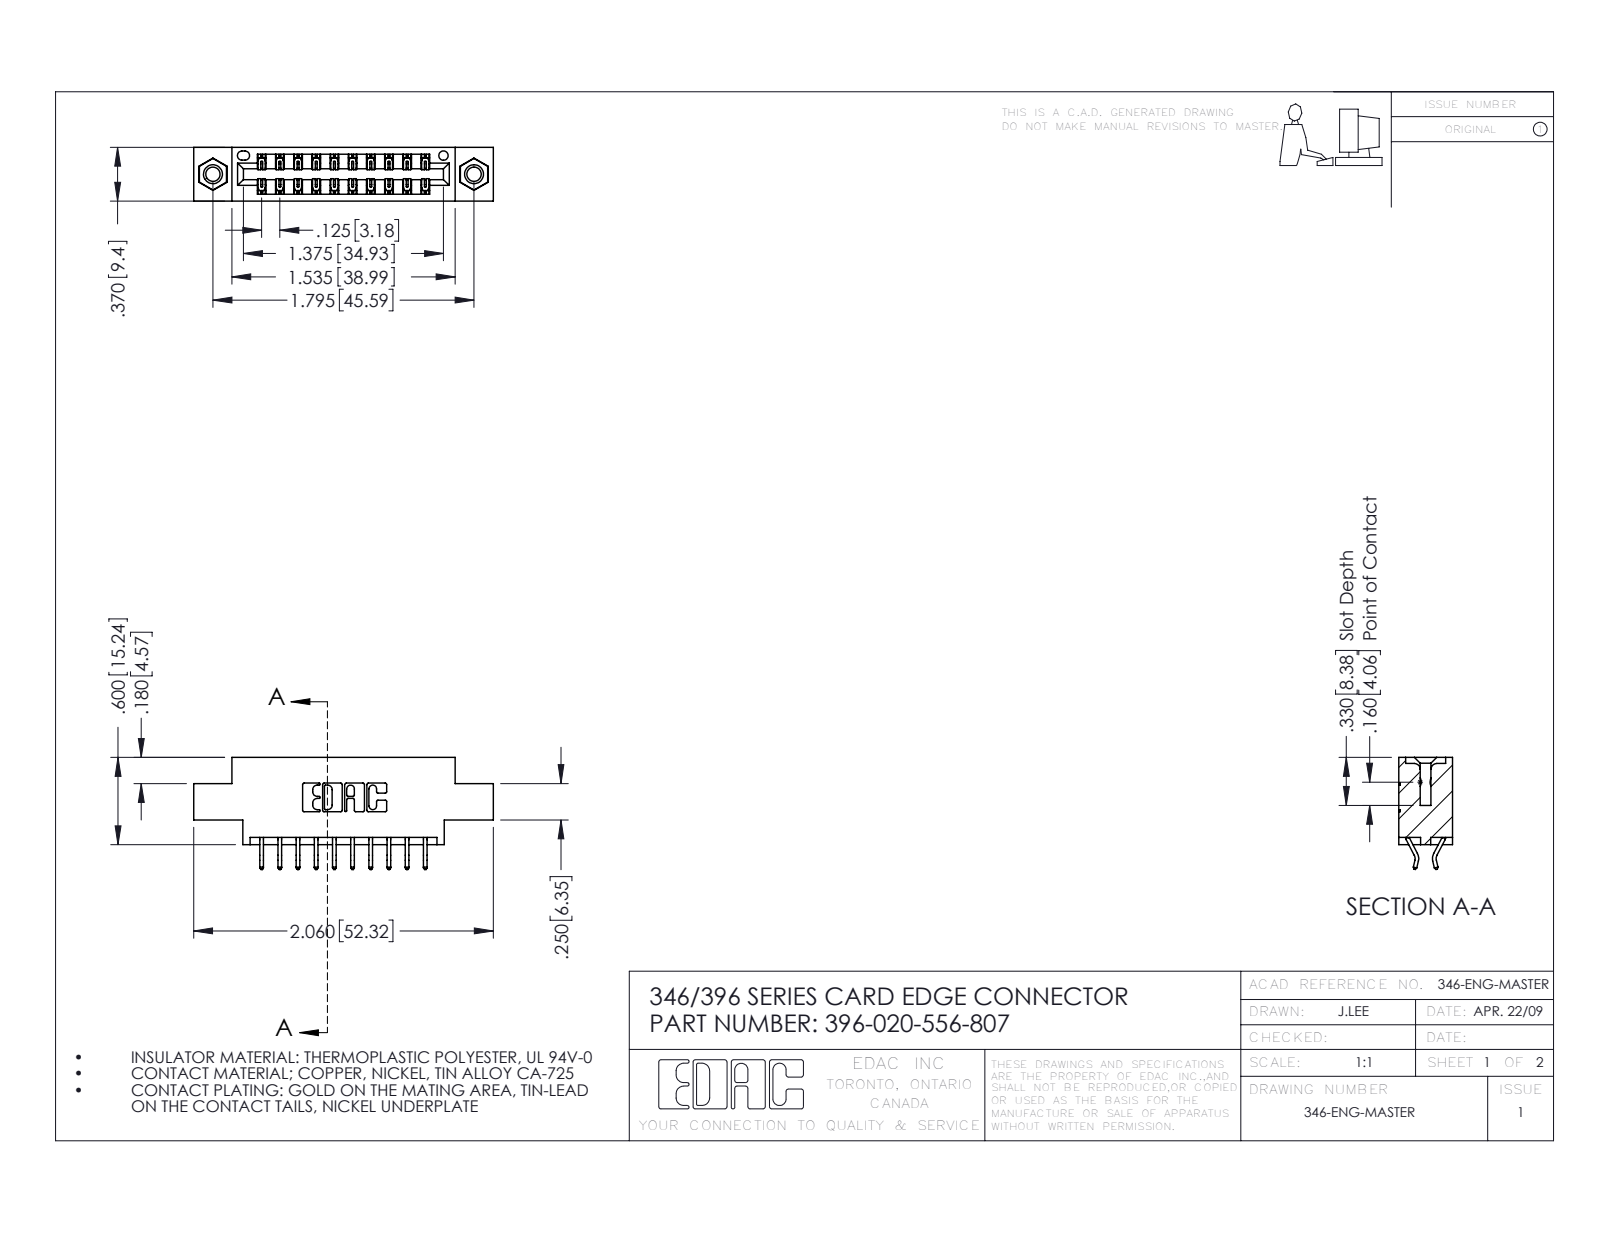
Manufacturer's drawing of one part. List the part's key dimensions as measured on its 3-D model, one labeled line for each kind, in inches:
Part name (STEP PRODUCT): 346 Part_0.170 Offset - 0.156 Dia-TI; 345-292-001_556 Tail; 396-020-556-807; 345-250-001_345-250-005-103
STEP written by: SolidWorks 2016 (CONFIG_CONTROL_DESIGN)
Units: inches
Bodies: 23 solids, 1346 faces (892 planar, 438 cylindrical, 16 other)
Overall size (bounding box): 2.06 × 0.77 × 0.37
Volume: 0.286 in³ · Surface area: 9.504 in²
Round holes (diameter × count): ⌀0.098 ×2, ⌀0.125 ×2, ⌀0.156 ×2, ⌀0.064 ×1
Round bosses / shafts (diameter × count): ⌀0.155 ×2
Partial cylindrical surfaces — rounded edges, fillets, slot ends (radius × count): R0.006 ×30, R0.01 ×22, R0.007 ×6, R0.031 ×6, R0.026 ×3, R0.01 ×2, R0.014 ×2, R0.022 ×2
Main face-to-face distances: 0.25, 0.37, 0.048, 0.322, 0.222, 0.025, 0.148, 0.072, 0.298, 0.1
Hole centre spacings: 0.246, 1.59, 1.795
